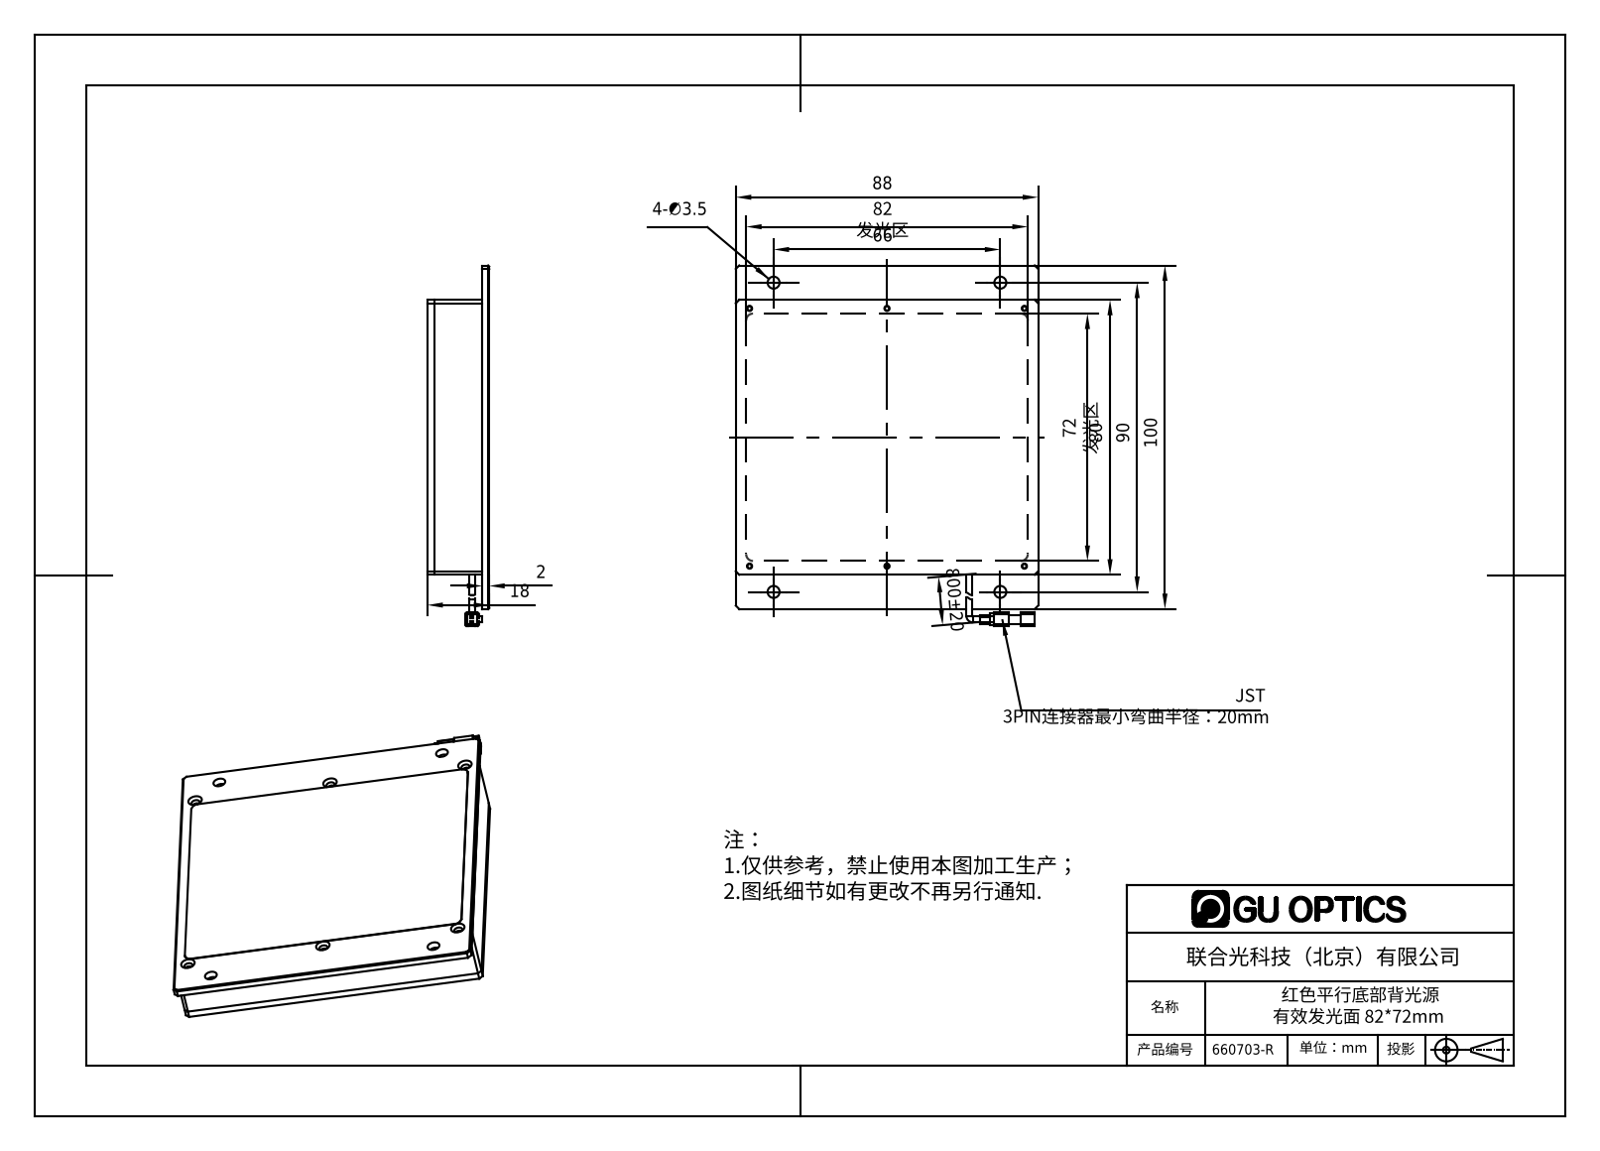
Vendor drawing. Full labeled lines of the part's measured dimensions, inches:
Part name (STEP PRODUCT): 660703-R
STEP written by: SolidWorks 2016 (AUTOMOTIVE_DESIGN)
Units: inches
Bodies: 5 solids, 419 faces (188 planar, 132 cylindrical, 99 other)
Overall size (bounding box): 4.134 × 3.465 × 0.713
Volume: 2.898 in³ · Surface area: 69.84 in²
Round holes (diameter × count): ⌀0.049 ×12, ⌀0.063 ×12, ⌀0.059 ×6, ⌀0.094 ×6, ⌀0.11 ×6, ⌀0.138 ×4, ⌀0.142 ×1
Round bosses / shafts (diameter × count): ⌀0.069 ×2
Partial cylindrical surfaces — rounded edges, fillets, slot ends (radius × count): R0.02 ×8, R0.039 ×8, R0.079 ×4, R0.059 ×2
Main face-to-face distances: 0.079, 0.63, 0.551, 0.083, 0.634, 0.713, 0.709, 0.157, 0.118, 2.992
Hole centre spacings: 1.575, 3.15, 3.364, 0.02, 2.972, 0.39, 0.404, 1.328
